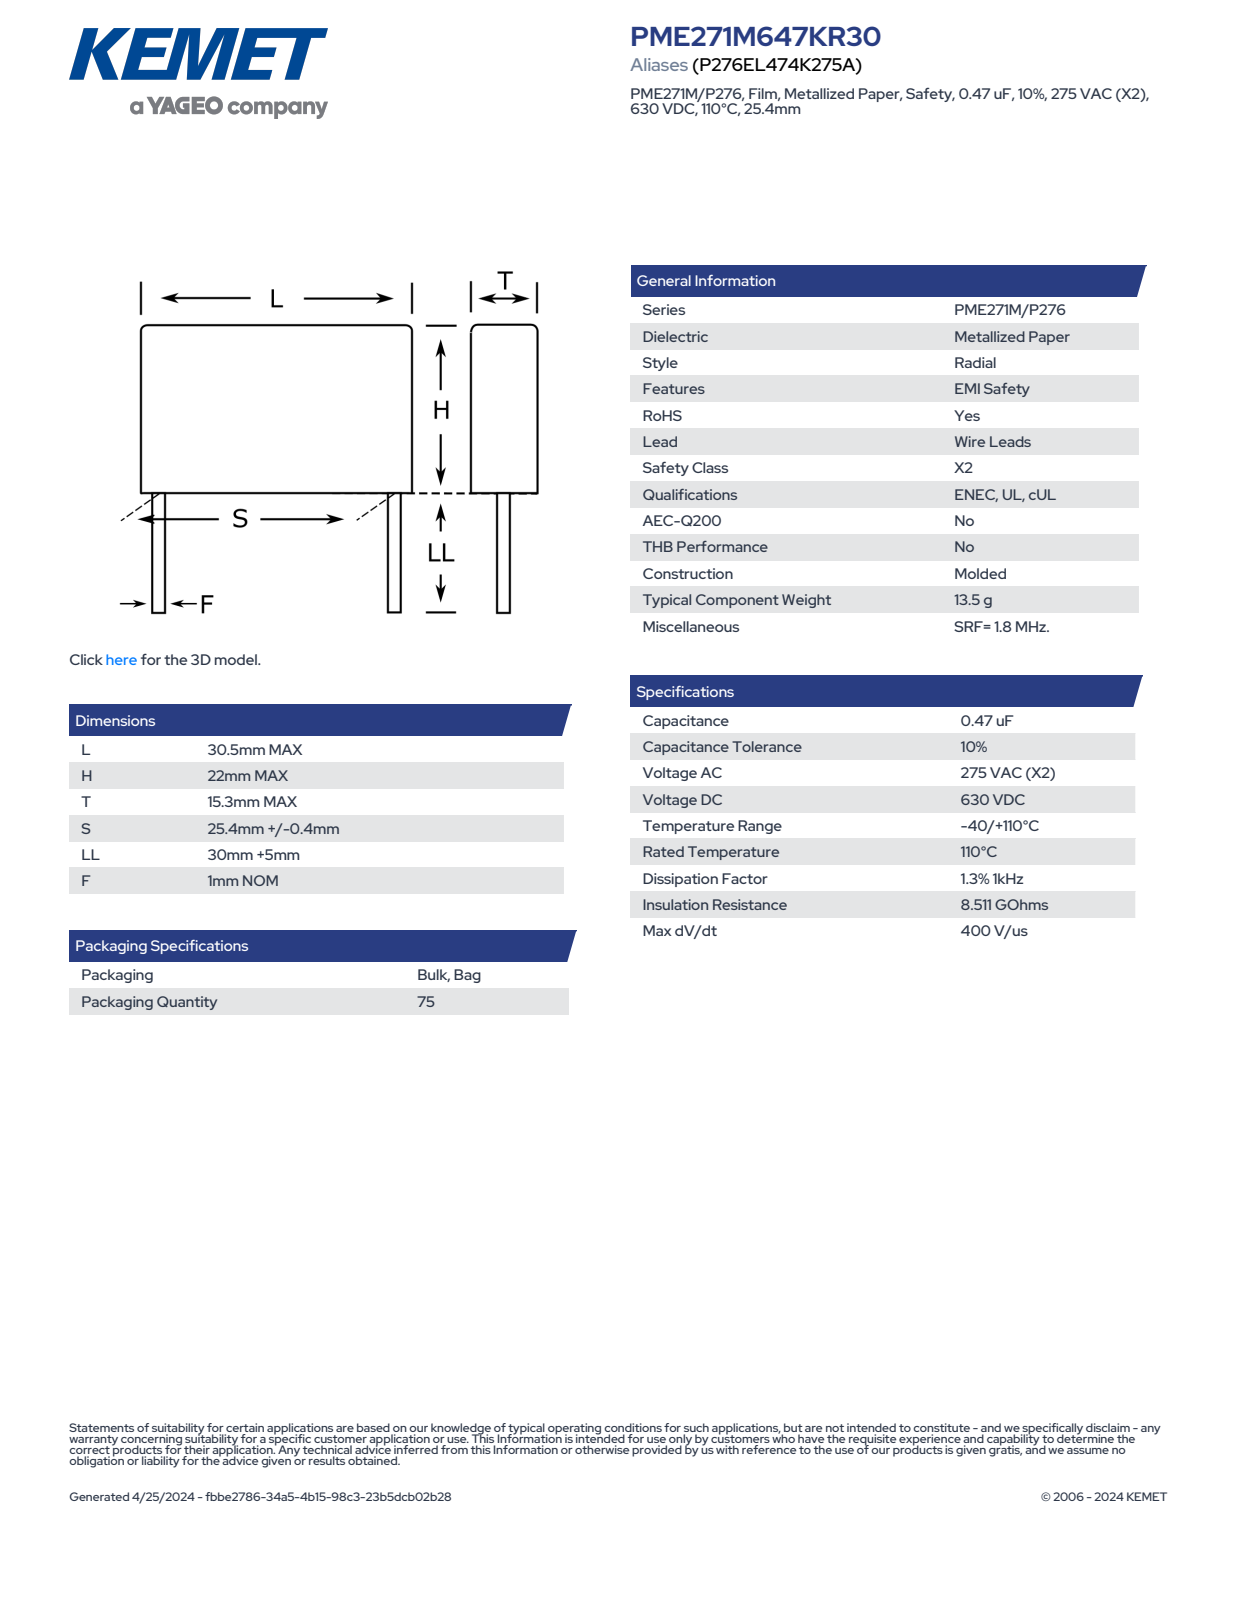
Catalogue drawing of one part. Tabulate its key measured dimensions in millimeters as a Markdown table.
| quantity | value |
| --- | --- |
| part name | CFR_MOLDED_30.5X22X15.3_L30.5H22T15.3S25.4LL35F1 |
| STEP written by | SolidWorks 2014 (AUTOMOTIVE_DESIGN) |
| units | millimeters |
| bodies | 4 solids, 73 faces (65 planar, 8 cylindrical, 0 other) |
| overall size | 57 × 30.5 × 15.3 |
| volume | 10 317 mm³ |
| surface area | 3 193 mm² |
| round bosses / shafts (diameter × count) | 1 × 2 |
| partial cylindrical surfaces (radius × count) | 0.5 × 4 |
| main face-to-face distances | 15.3, 22, 30.5, 15.31, 35, 57, 46.96, 11.96, 10.04, 44.22 |
